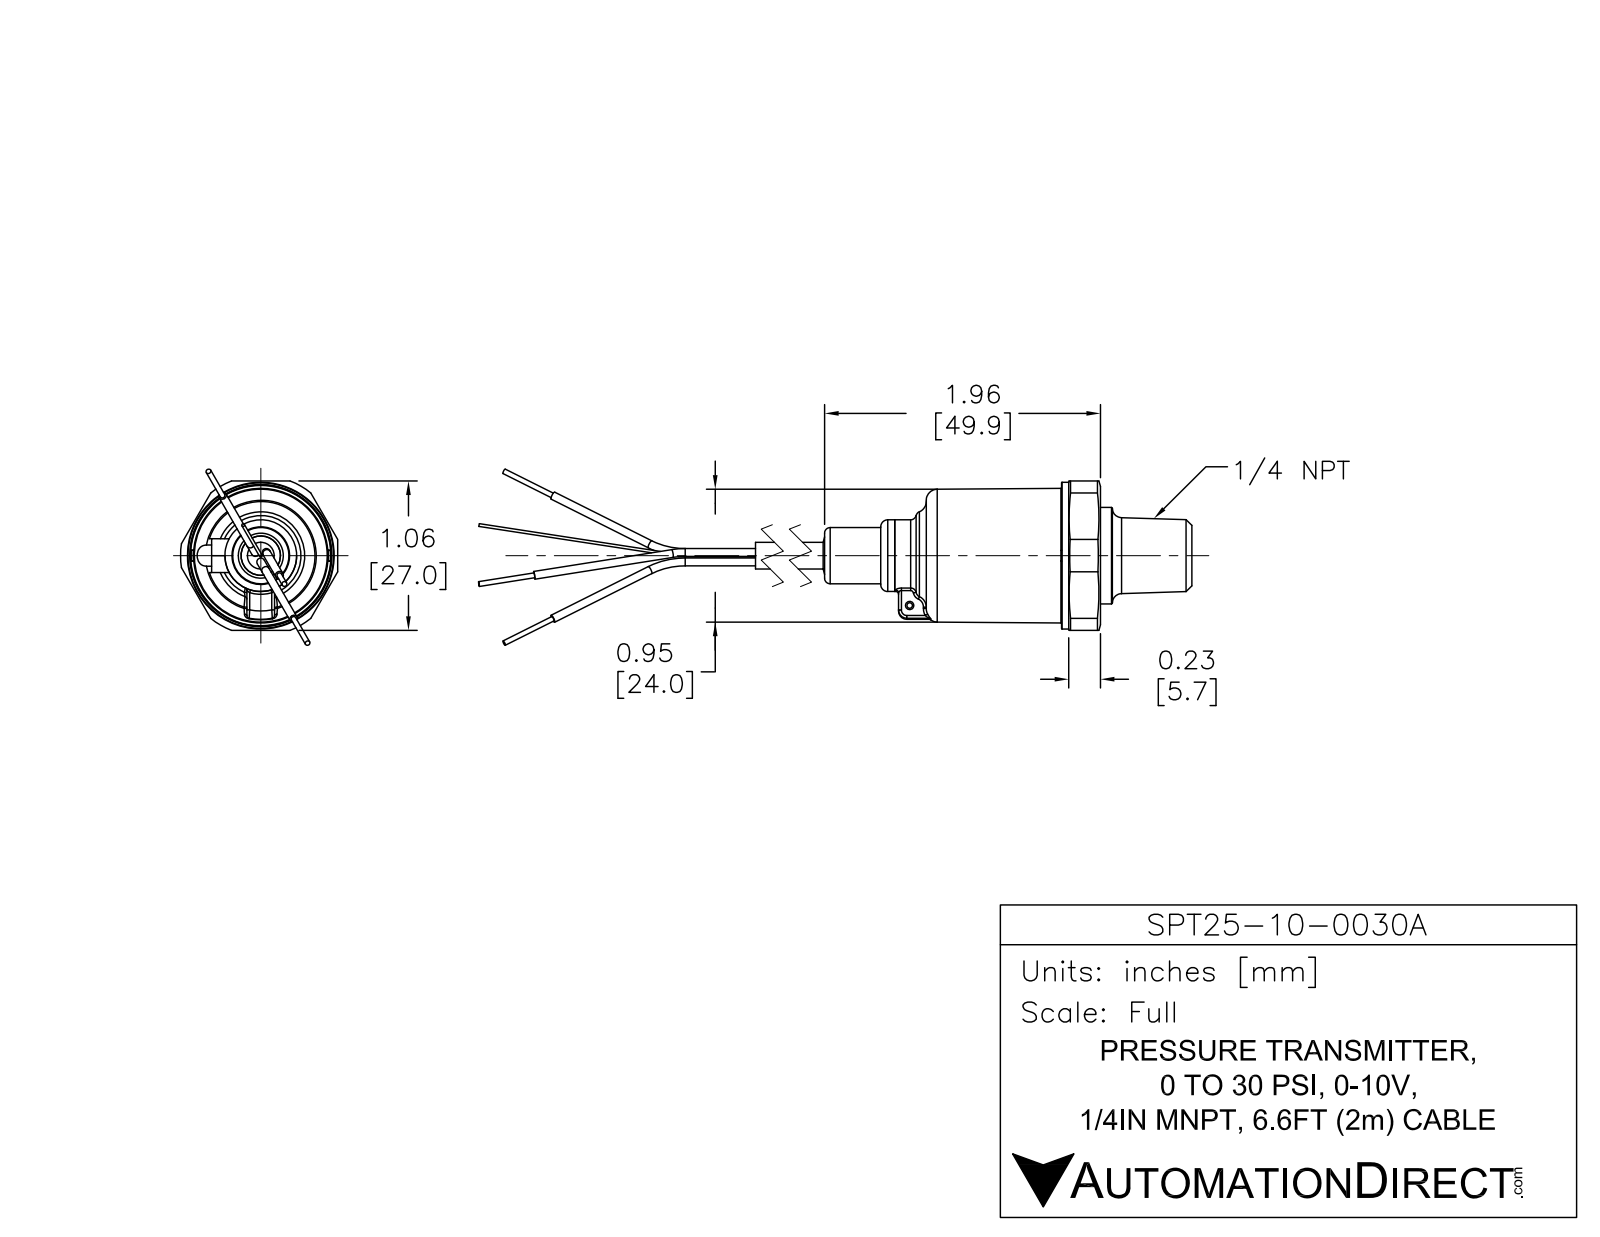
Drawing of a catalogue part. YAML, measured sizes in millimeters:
part_name: "SPT25-10-0030A"
step_written_by: "SolidWorks 2017 (AUTOMOTIVE_DESIGN)"
units: millimeters
bodies: {solids: 7, faces: 116, planar: 32, cylindrical: 49, other: 35}
overall_size: [153.3, 29, 27.09]
volume: 20801
surface_area: 7170
round_holes:
  - {diameter: 1, count: 1}
  - {diameter: 3.3, count: 1}
round_bosses_or_shafts:
  - {diameter: 1.4, count: 6}
  - {diameter: 0.75, count: 5}
  - {diameter: 26.75, count: 1}
  - {diameter: 24, count: 1}
  - {diameter: 17.5, count: 1}
  - {diameter: 14, count: 1}
  - {diameter: 13, count: 1}
  - {diameter: 10, count: 1}
partial_cylinders:
  - {radius: 2, count: 1}
  - {radius: 14.5, count: 1}
face_to_face_distances: [6.75, 24, 17.25, 42.75, 49.5, 66.75, 44, 1.25, 5.5, 22.75]
